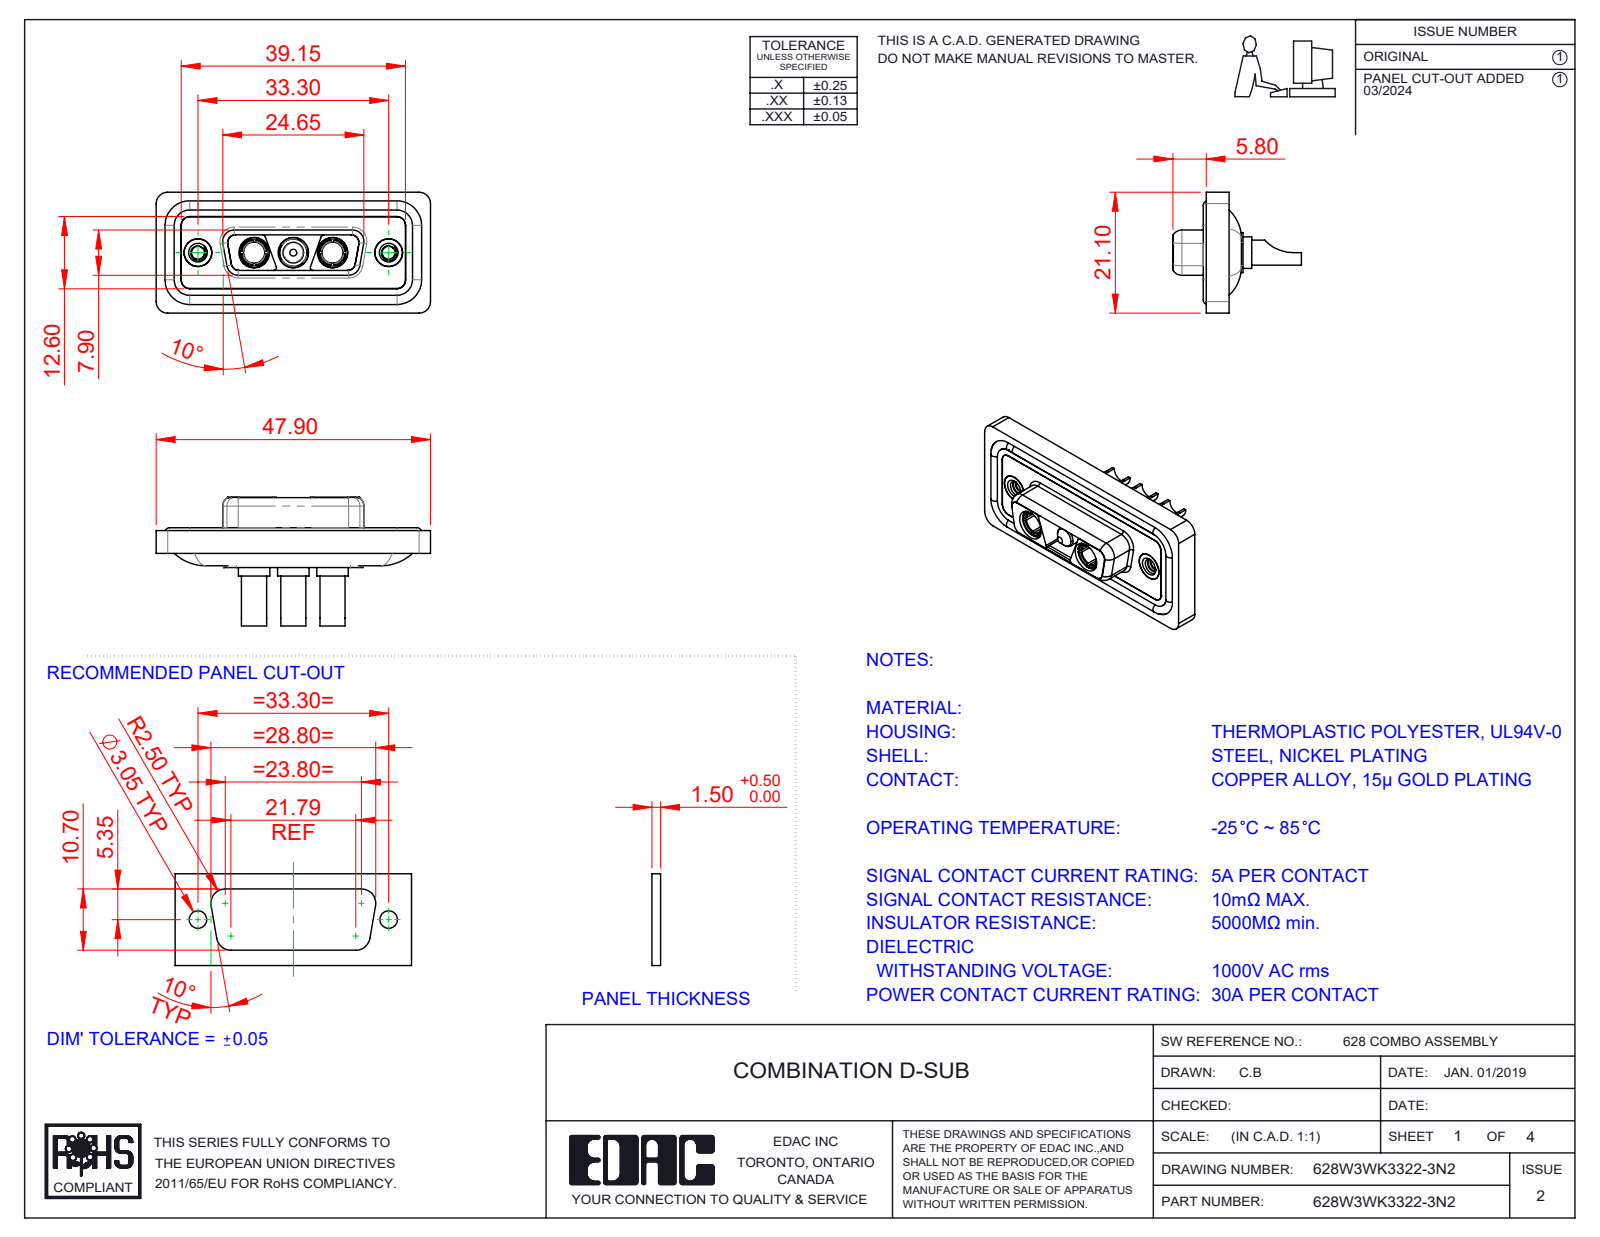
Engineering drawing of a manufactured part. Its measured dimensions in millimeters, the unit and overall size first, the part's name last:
Units: millimetres
Overall size (bounding box): 47.9 × 22.45 × 21.1
Round holes (diameter × count): ⌀4.85 ×5, ⌀3.5 ×3, ⌀5.3 ×3, ⌀2.26 ×2, ⌀3.7 ×2, ⌀4 ×2, ⌀4.05 ×2, ⌀5 ×2
Round bosses / shafts (diameter × count): ⌀1.6 ×4, ⌀5.5 ×3, ⌀5.2 ×3, ⌀4.75 ×3, ⌀4.4 ×3, ⌀3.75 ×3, ⌀4.96 ×2, ⌀4.95 ×2
Partial cylindrical surfaces — rounded edges, fillets, slot ends (radius × count): R1.5 ×22, R2 ×20, R1.35 ×12, R0.5 ×8, R1.6 ×8, R0.25 ×4, R0.6 ×4, R0.65 ×4
Main face-to-face distances: 0.4, 1.6, 0.5, 1.1, 2.9, 1.8, 5.65, 7.05, 5.35, 6.6
Hole centre spacings: 6.85, 9.8, 16.65, 23.5, 13.7, 33.3
Volume: 5 950 mm³ · Surface area: 9 827 mm²
Bodies: 13 solids, 601 faces (187 planar, 267 cylindrical, 147 other)
Part name (STEP PRODUCT): Power Pin_30A SC; 628Combo Threaded Rivet_2; Power Socket_30A SC; 628Combo Shell Front_15 Contacts (+4 more)
STEP written by: SolidWorks 2023 (CONFIG_CONTROL_DESIGN)
